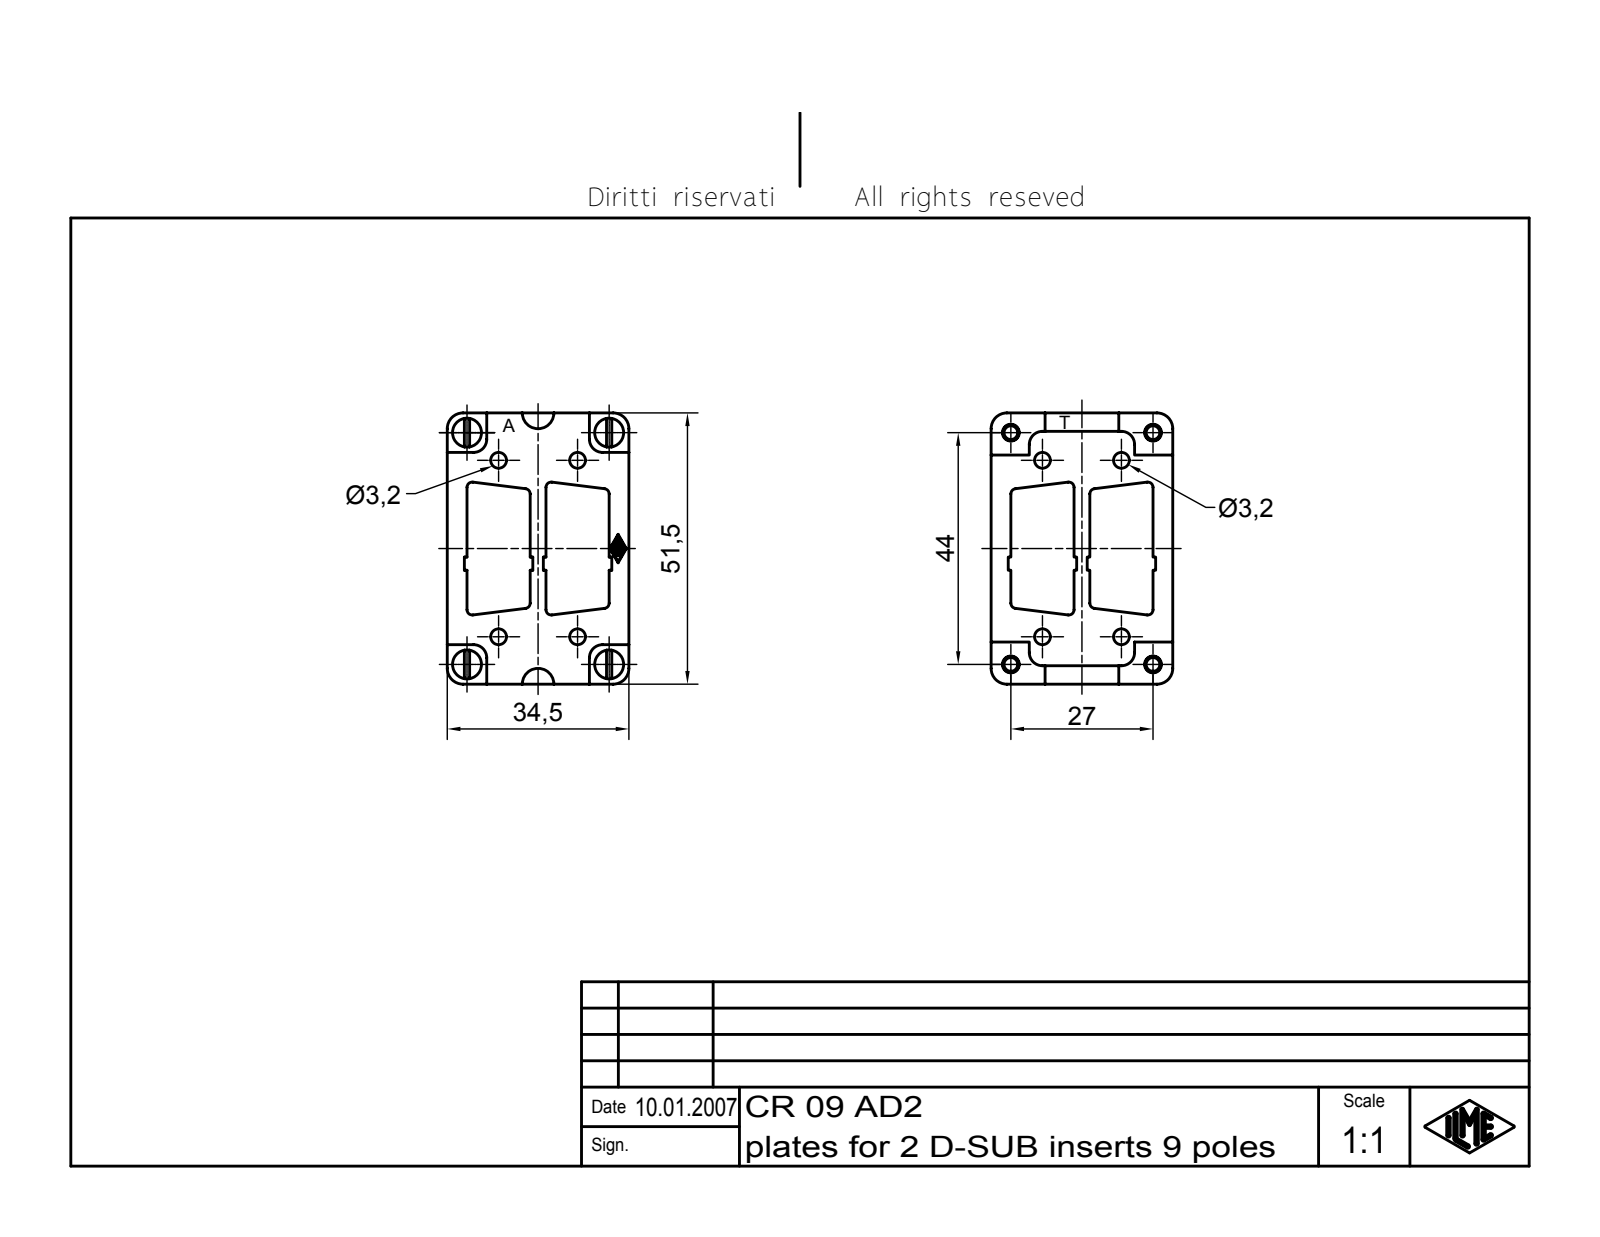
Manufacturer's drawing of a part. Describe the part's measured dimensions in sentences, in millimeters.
The part is named "CR 09 AD2". Its 3-D file was written by "Autodesk Inventor 7 (AUTOMOTIVE_DESIGN)". It is 1 solid with 215 faces: 129 planar, 70 cylindrical and 16 other. Overall it measures 51.5 by 34.5 by 14 millimeters. Its volume is 5 658 cubic millimeters and its surface area 5 496 square millimeters. Round holes: 4 of diameter 3, 4 of diameter 3.2. Round bosses or shafts: 4 of diameter 5.5, 4 of diameter 3. Partial cylindrical surfaces (rounded edges, fillets, slot ends): 14 of radius 0.1, 8 of radius 1, 8 of radius 2.5, 6 of radius 3. The main face-to-face distances are 3, 8, 7, 2, 10, 51.5, 3.5, 43.5, 34.5, 1. The hole center spacings are 7.97, 21.65, 39.21, 44.07, 15, 27, 33.5, 36.7.
